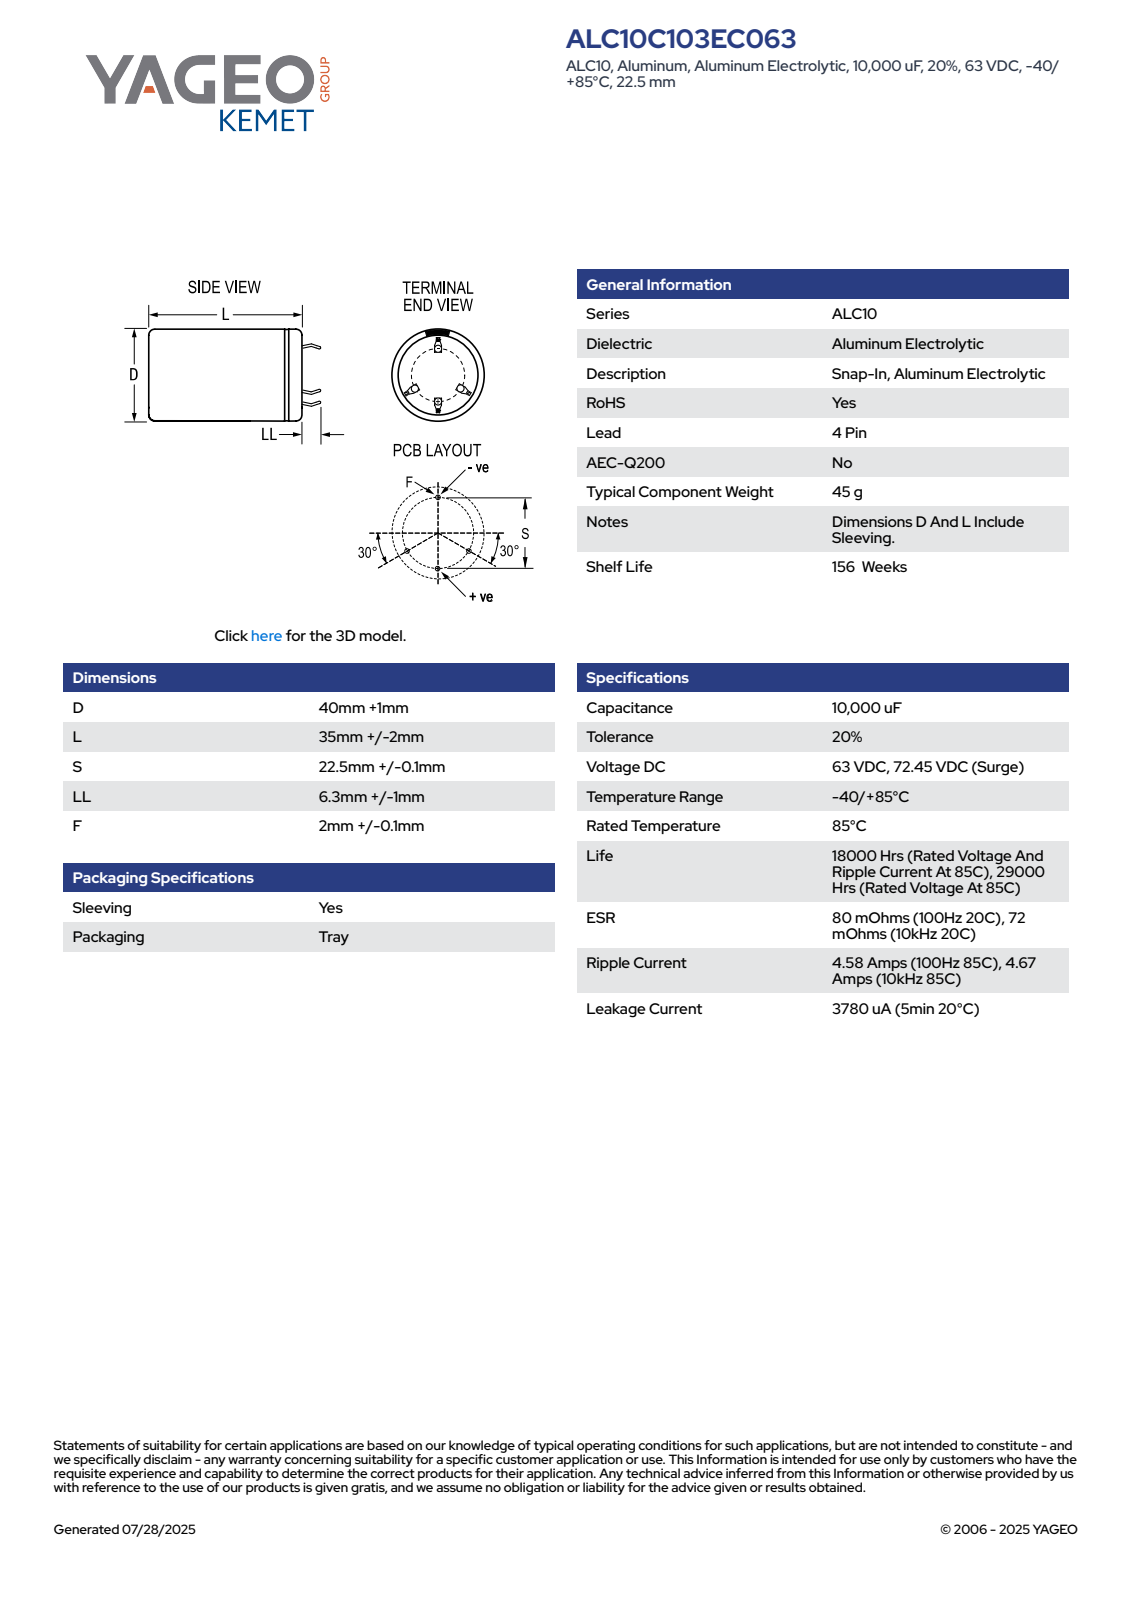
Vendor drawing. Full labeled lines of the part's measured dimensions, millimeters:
Part name (STEP PRODUCT): CARS_K4P_40X35_D41L37S22.5LL7.3F2.1
STEP written by: SolidWorks 2014 (AUTOMOTIVE_DESIGN)
Units: millimetres
Bodies: 1 solid, 134 faces (80 planar, 15 cylindrical, 39 other)
Overall size (bounding box): 44.29 × 41 × 41
Volume: 48 078 mm³ · Surface area: 7 449 mm²
Round holes (diameter × count): ⌀36.28 ×1
Round bosses / shafts (diameter × count): ⌀41 ×1
Partial cylindrical surfaces — rounded edges, fillets, slot ends (radius × count): R20.49 ×1
Main face-to-face distances: 36.99, 37.49, 0.5, 0.42, 0.6, 20.47, 0.75, 1.35, 20.05, 20.89
